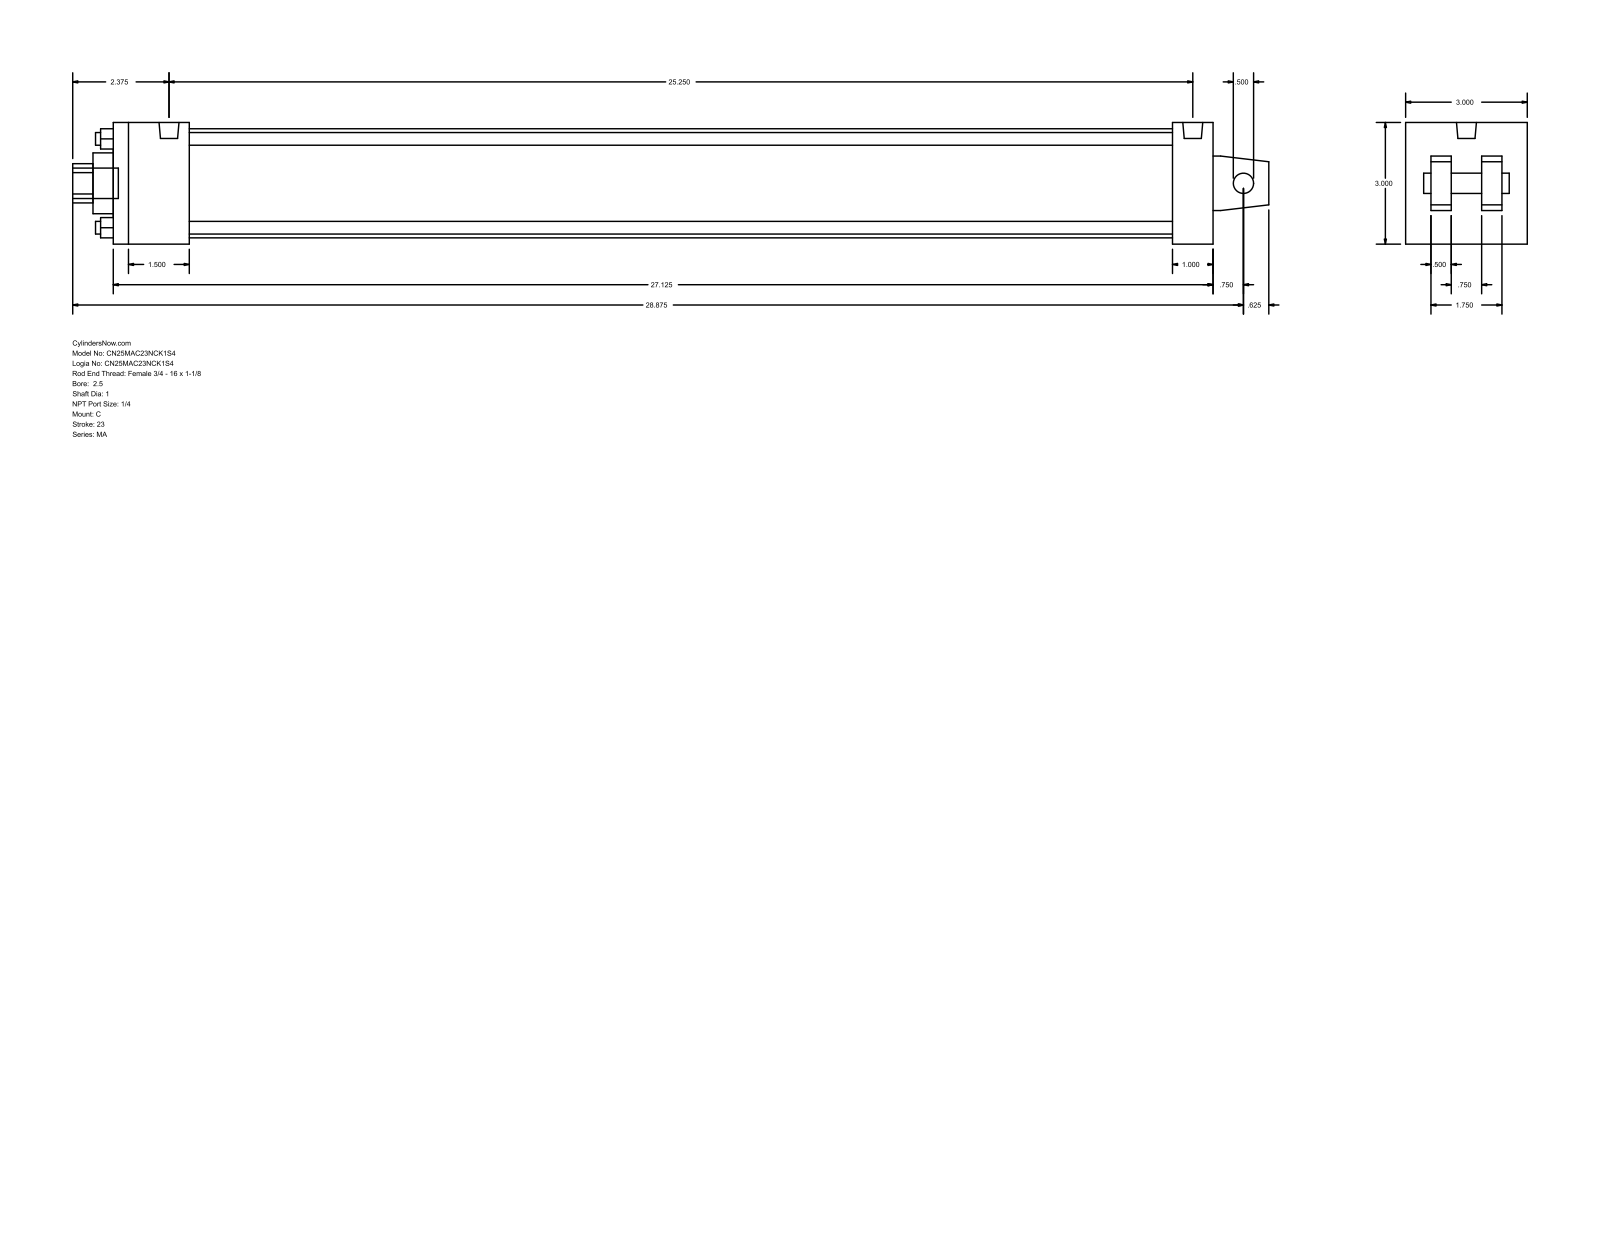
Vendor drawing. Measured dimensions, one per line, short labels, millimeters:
name: MA_C__0250_1
written by: GSSL Pune (CONFIG_CONTROL_DESIGN)
unit: mm
bodies: 0 solids, 103 faces (76 planar, 27 cylindrical, 0 other)
size: 749.3 × 76.2 × 76.2
holes: 4× ⌀7.94, 1× ⌀12.7, 1× ⌀25.4, 1× ⌀38.1, 1× ⌀68.33
bosses: 4× ⌀7.94, 2× ⌀12.49, 1× ⌀19.05
rounds: 1× R12.29
face distances: 76.2, 688.98, 47.63, 12.7, 15.87, 60.33, 25.4, 28.57, 663.58, 615.95
hole spacings: 39.33, 55.62, 78.66
